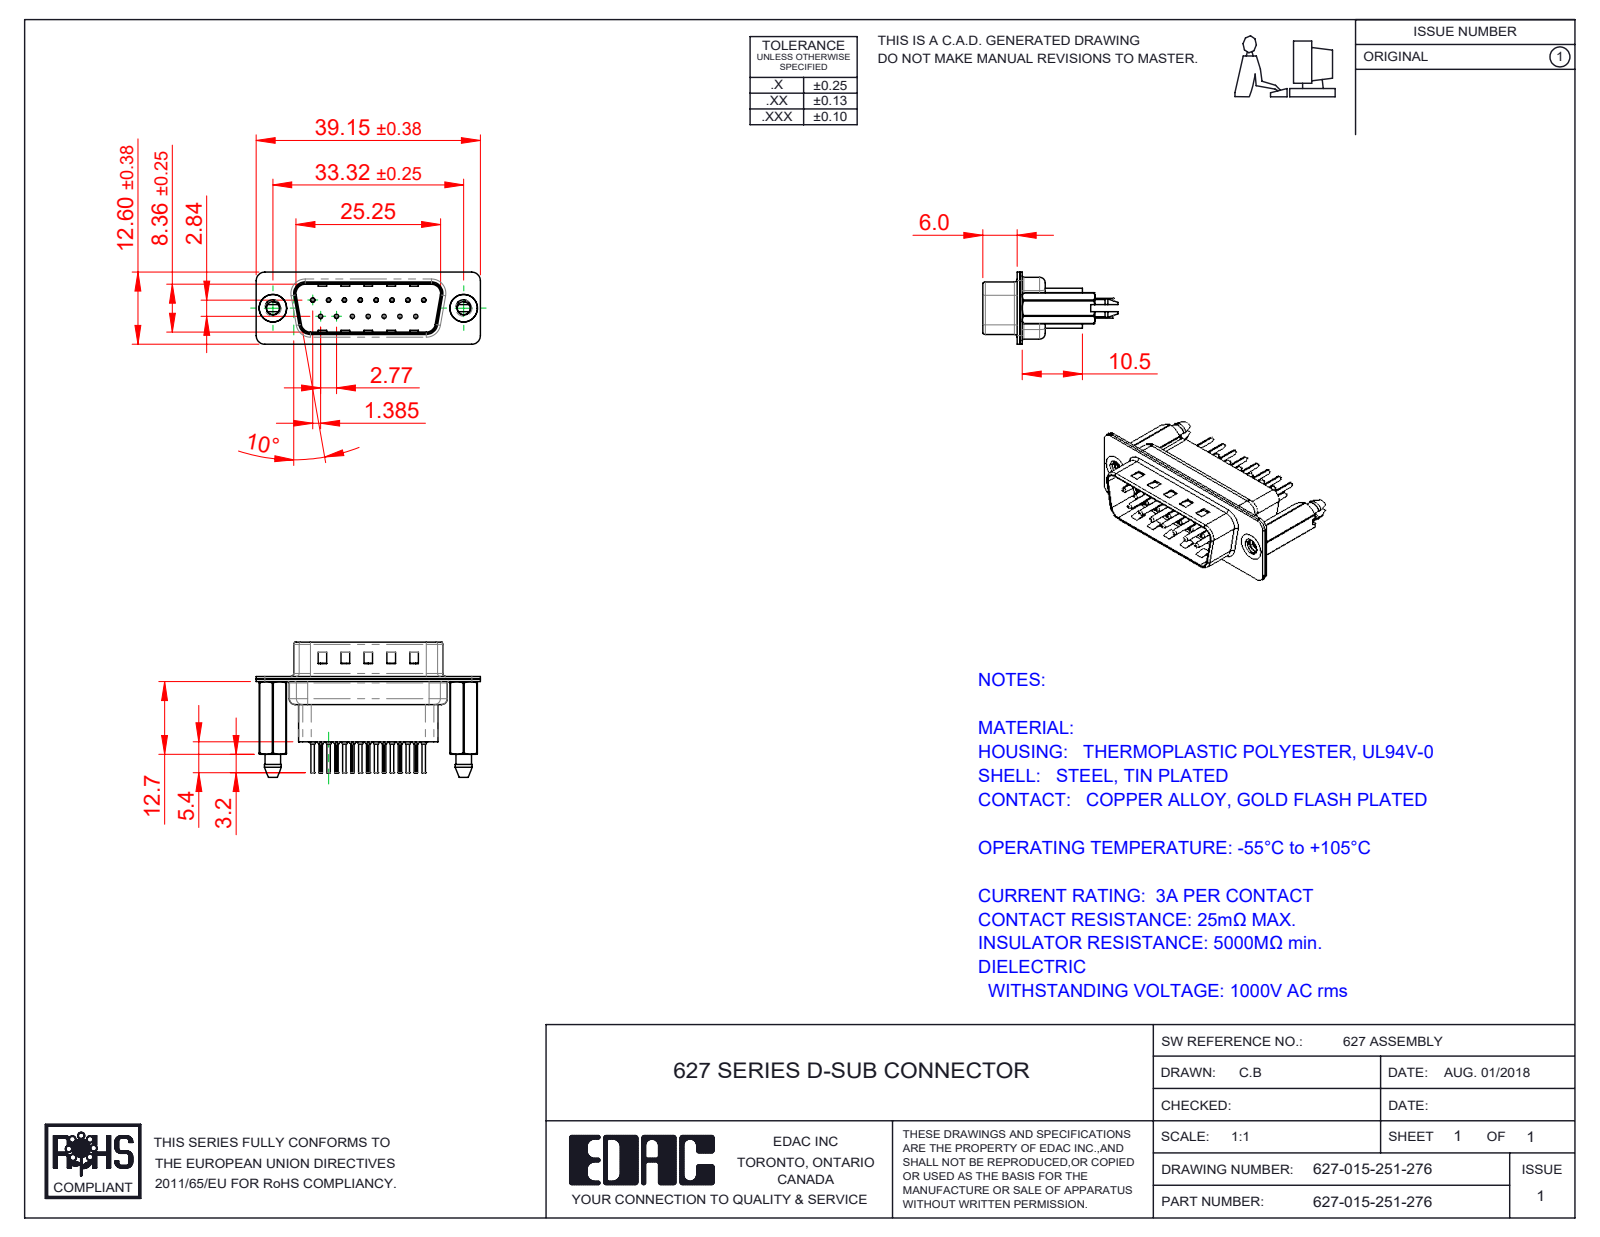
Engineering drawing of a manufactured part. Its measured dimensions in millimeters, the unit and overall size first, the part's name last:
Units: millimetres
Overall size (bounding box): 39.15 × 23.6 × 12.6
Round holes (diameter × count): ⌀0.2 ×15, ⌀0.35 ×15, ⌀1.1 ×15, ⌀1.6 ×15, ⌀2.26 ×2, ⌀4 ×2, ⌀4.8 ×2
Round bosses / shafts (diameter × count): ⌀2 ×15, ⌀1.5 ×15, ⌀0.75 ×15, ⌀0.6 ×15, ⌀4.9 ×2
Partial cylindrical surfaces — rounded edges, fillets, slot ends (radius × count): R0.1 ×30, R1.5 ×18, R2 ×12, R1.6 ×10, R0.5 ×8, R0.25 ×4, R0.6 ×4, R0.65 ×4
Main face-to-face distances: 0.4, 0.45, 0.9, 0.82, 9.58, 1.5, 0.68, 7.68, 4.76, 1.4
Hole centre spacings: 3.16, 2.77, 5.54, 8.31, 11.08, 5.03, 5.04, 7.48
Volume: 2 858 mm³ · Surface area: 7 369 mm²
Bodies: 20 solids, 1918 faces (531 planar, 754 cylindrical, 633 other)
Part name (STEP PRODUCT): 627 Contact Row 1_41; 627 Shell Rear_15 Contacts; 627-015-251-276; 627 Shell Front_15 Contacts (+3 more)
STEP written by: SolidWorks 2020 (CONFIG_CONTROL_DESIGN)
